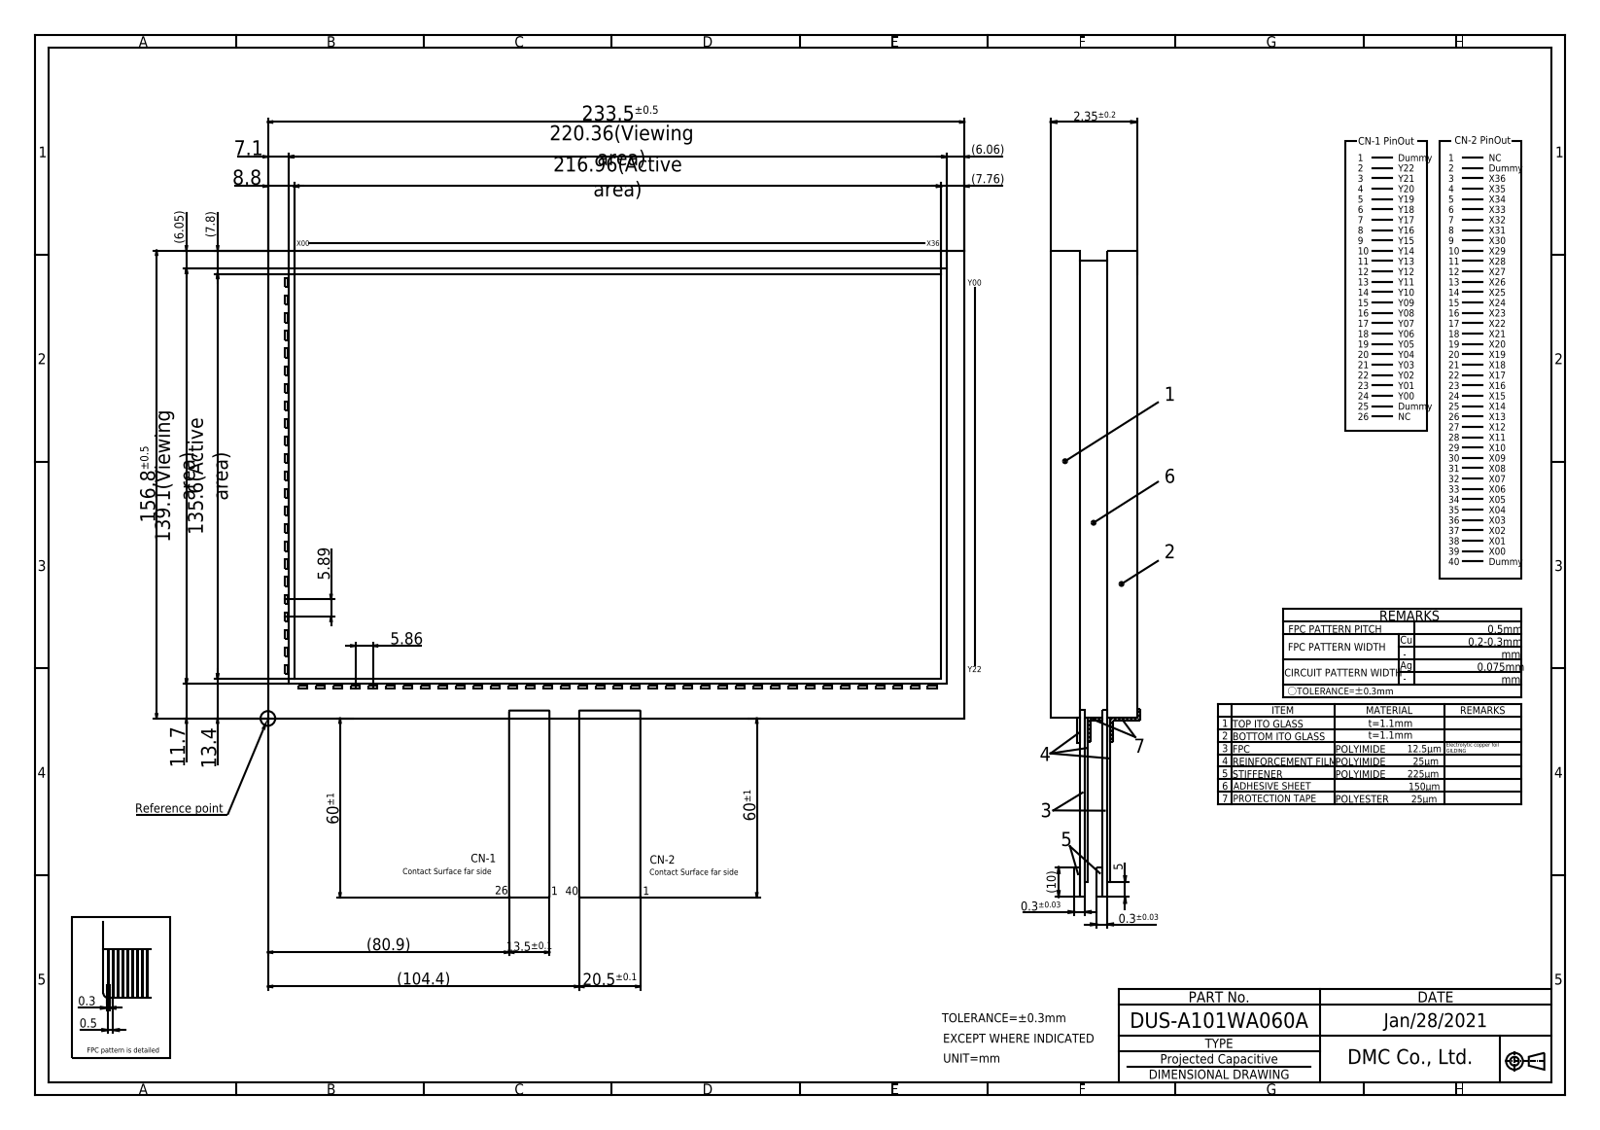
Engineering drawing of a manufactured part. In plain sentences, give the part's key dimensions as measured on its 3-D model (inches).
The part is named "DUS-A101WA060A". Its 3-D file was written by "Autodesk Inventor 2020 (CONFIG_CONTROL_DESIGN)". It is 1 solid with 302 faces: 298 planar, 4 cylindrical and 0 other. Overall it measures 12.87 by 9.77 by 0.093 inches. Its volume is 5.262 cubic inches and its surface area 123 square inches. Partial cylindrical surfaces (rounded edges, fillets, slot ends): 4 of radius 0.008. The main face-to-face distances are 0.093, 0.045, 0.048, 0.049, 0.043, 0.044, 0.039, 0.089, 6.173, 9.193.
